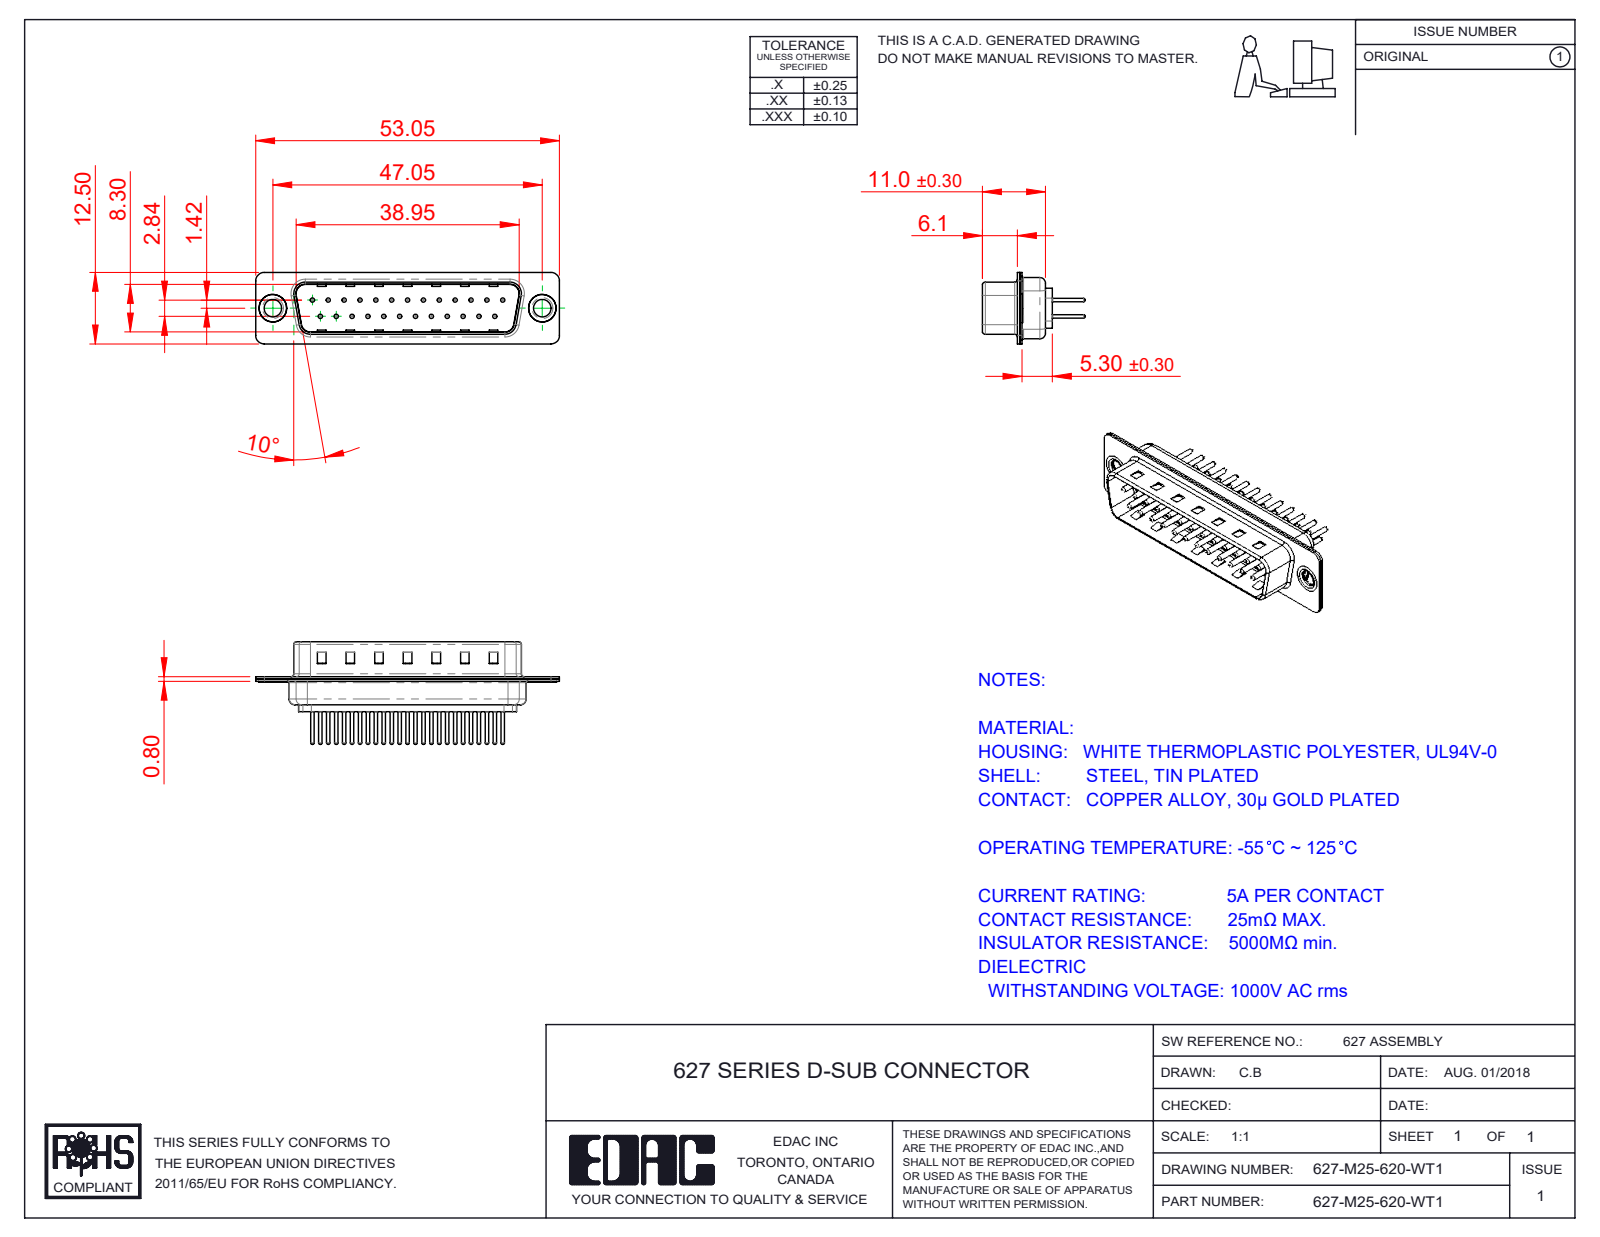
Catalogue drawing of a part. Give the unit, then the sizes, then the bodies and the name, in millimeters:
Units: millimetres
Overall size (bounding box): 53.05 × 17.9 × 12.5
Round holes (diameter × count): ⌀0.75 ×25, ⌀1.6 ×25, ⌀2 ×25, ⌀3.05 ×2, ⌀4 ×2, ⌀4.8 ×2
Round bosses / shafts (diameter × count): ⌀1.5 ×25, ⌀0.6 ×25, ⌀5 ×2, ⌀4.9 ×2, ⌀3.55 ×2
Partial cylindrical surfaces — rounded edges, fillets, slot ends (radius × count): R1.5 ×16, R2 ×12, R0.5 ×8, R1.6 ×8, R0.25 ×4, R0.6 ×4, R0.65 ×4, R0.9 ×4
Main face-to-face distances: 0.4, 0.8, 9.5, 9.1, 8.7, 9.9, 1.2, 6.1, 5.7, 0.75
Hole centre spacings: 3.16, 2.77, 5.54, 8.31, 11.08, 13.85, 16.62, 5.03
Volume: 2 641 mm³ · Surface area: 6 698 mm²
Bodies: 30 solids, 1275 faces (346 planar, 471 cylindrical, 458 other)
Part name (STEP PRODUCT): 627M Thru Hole Rivet; 627M Contact Row 2_20; 627M Shell Rear_25 Contacts; 627-M25-620-WT1 (+3 more)
STEP written by: SolidWorks 2020 (CONFIG_CONTROL_DESIGN)
